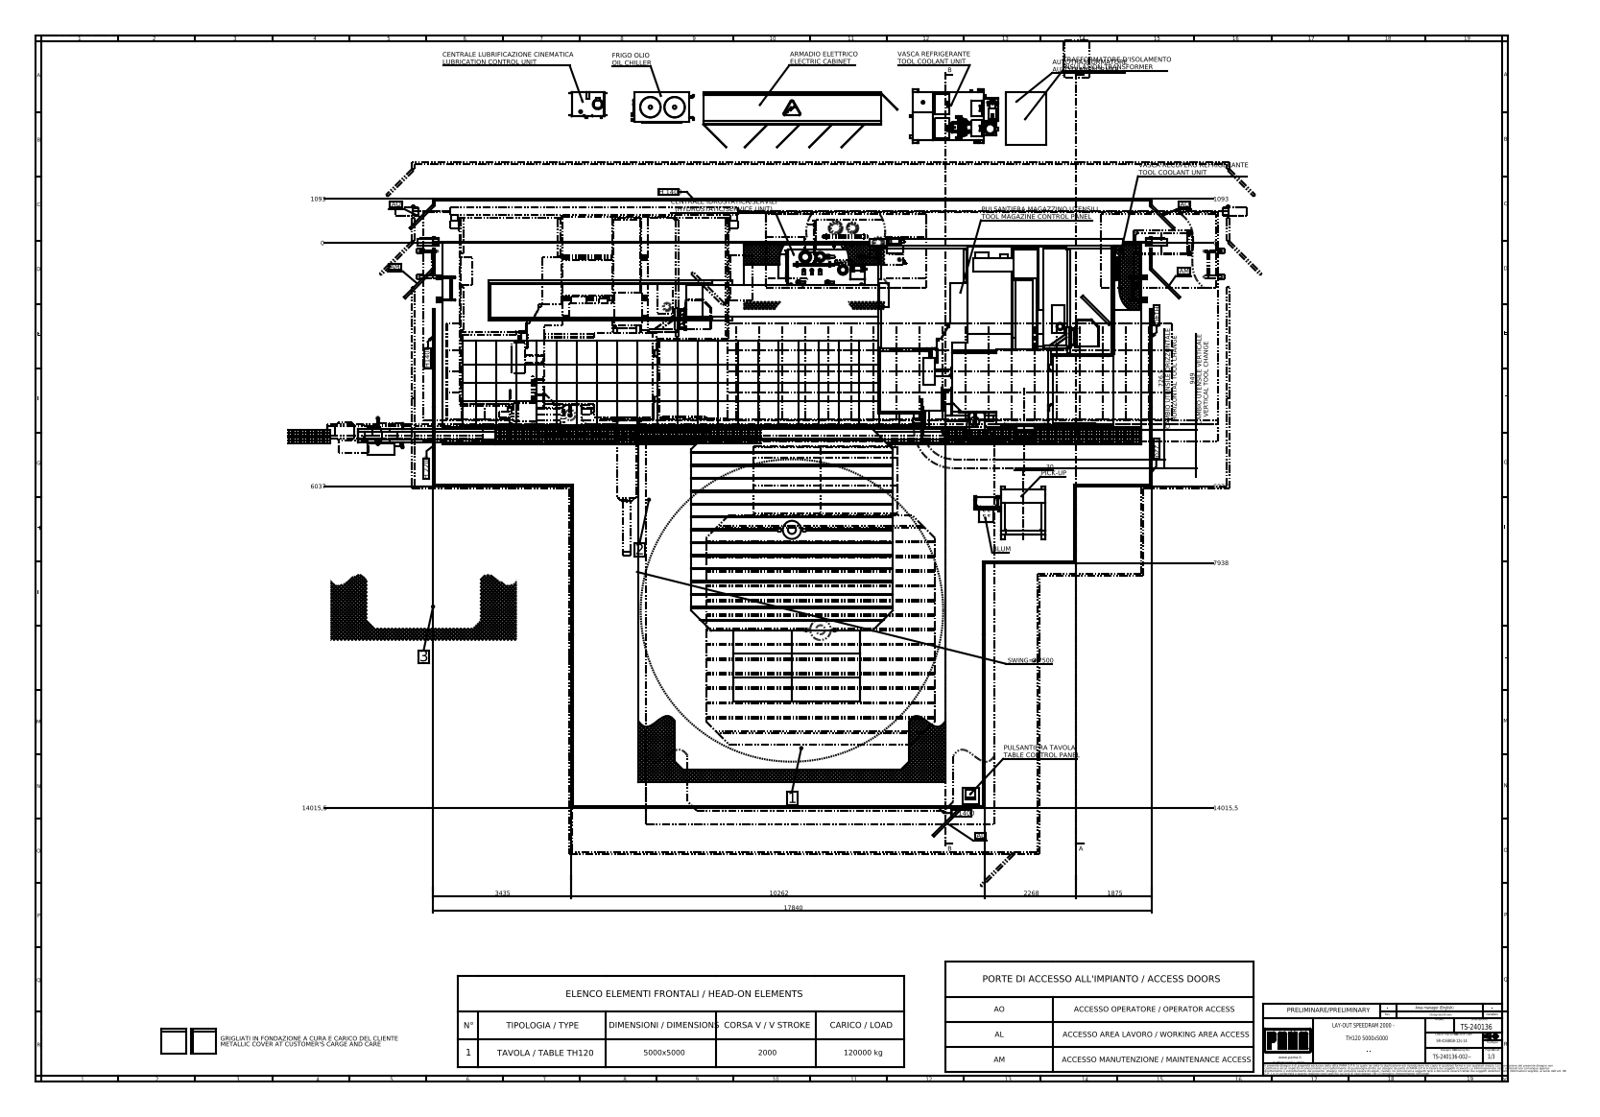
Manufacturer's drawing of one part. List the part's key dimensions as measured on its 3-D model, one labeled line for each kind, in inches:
Part name (STEP PRODUCT): S003249_TM 60-130; S003246_TM 60 - 130; S003244_SRAM 4-416; S003376_Y=4000 (+8 more)
STEP written by: SolidWorks 2023 (AUTOMOTIVE_DESIGN)
Units: inches
Bodies: 584 solids, 8930 faces (6043 planar, 2279 cylindrical, 608 other)
Overall size (bounding box): 840.157 × 818.106 × 392.165
Volume: 45 420 000 in³ · Surface area: 4 007 000 in²
Round holes (diameter × count): ⌀1.378 ×144, ⌀2.74 ×63, ⌀0.854 ×29, ⌀1.465 ×18, ⌀0.197 ×17, ⌀0.276 ×9, ⌀1.181 ×9, ⌀0.315 ×8, ⌀0.512 ×8, ⌀0.551 ×8, ⌀0.433 ×7, ⌀1.075 ×6
Round bosses / shafts (diameter × count): ⌀1.059 ×29, ⌀1.669 ×20, ⌀0.787 ×15, ⌀1.575 ×11, ⌀0.354 ×10, ⌀2.165 ×8, ⌀2.61 ×7, ⌀2.362 ×7
Partial cylindrical surfaces — rounded edges, fillets, slot ends (radius × count): R0.197 ×175, R0.394 ×63, R0.315 ×54, R0.591 ×53, R0.157 ×39, R0.236 ×26, R1.378 ×26, R0.079 ×21
Main face-to-face distances: 78.74, 1.969, 29.646, 49.094, 5.118, 24.528, 54.213, 0.394, 815.295, 840.157
Hole centre spacings: 10.753, 19.685, 48.644, 29.843, 56.047, 39.37, 5.118, 10.236
